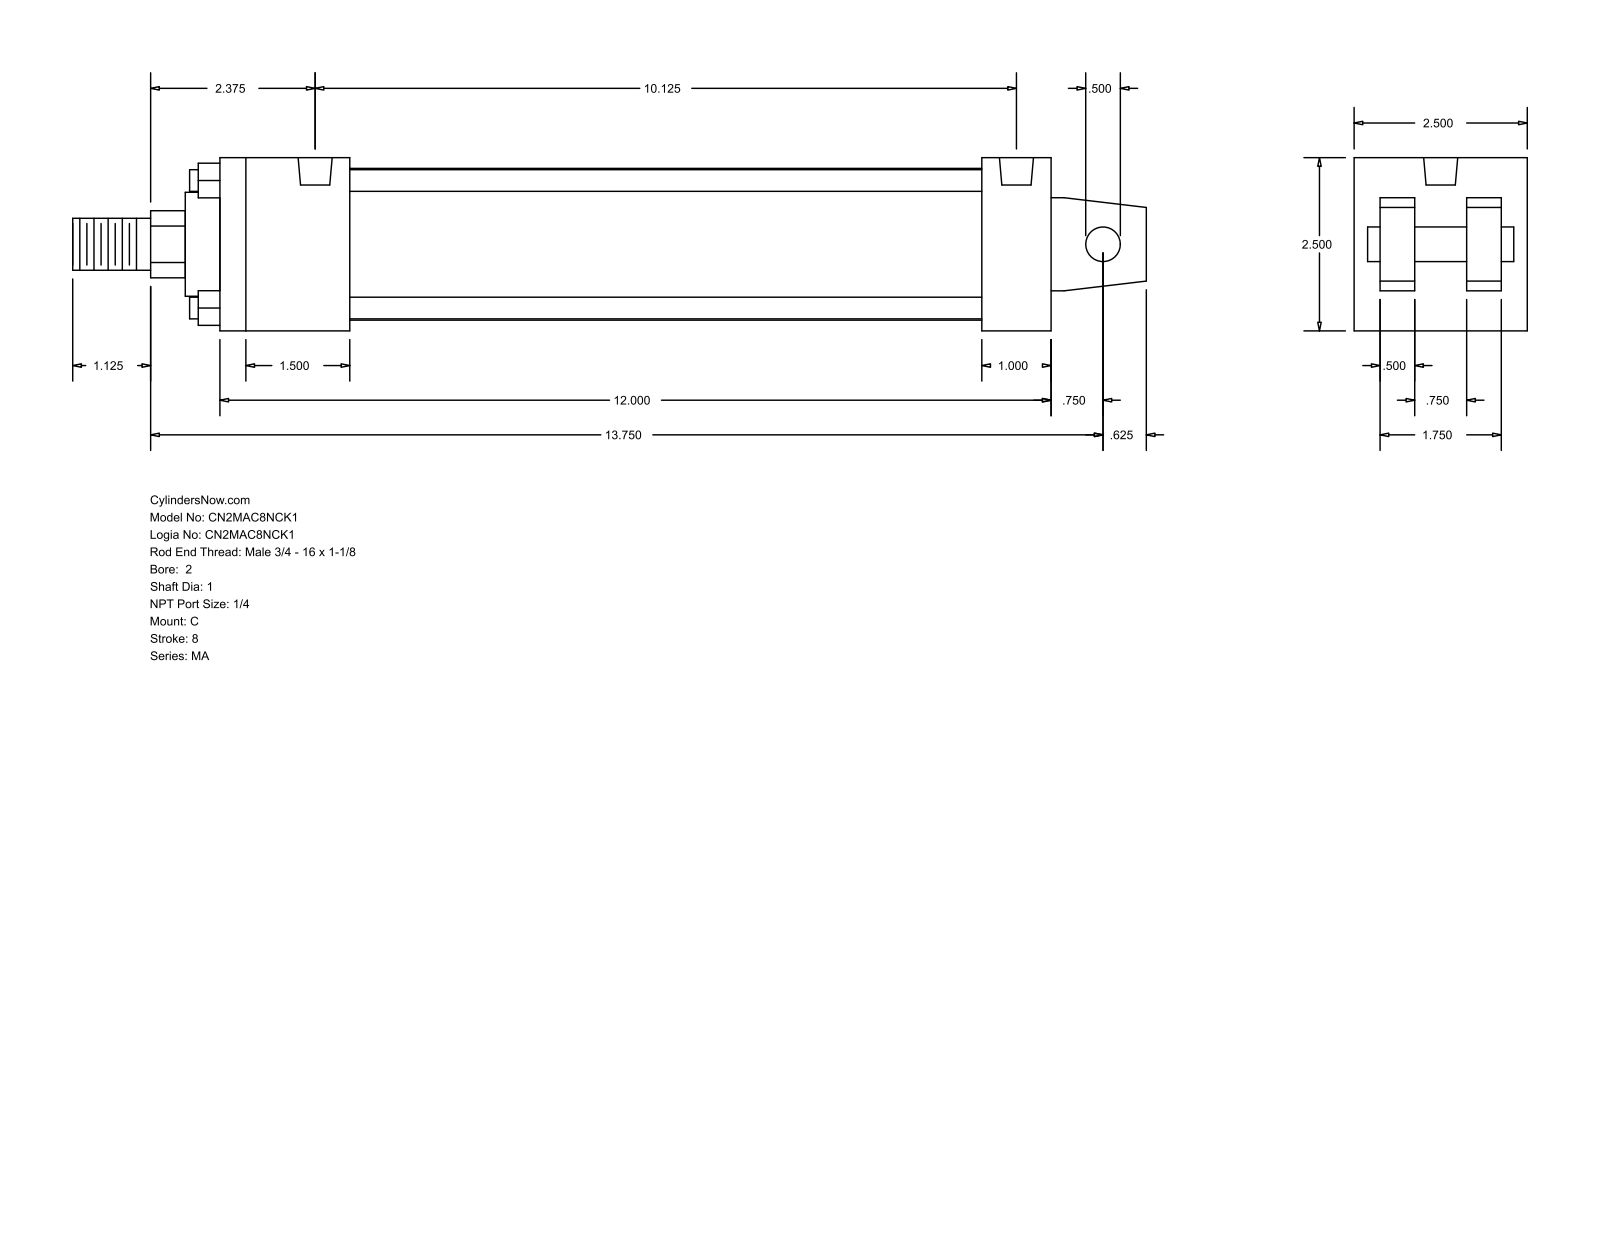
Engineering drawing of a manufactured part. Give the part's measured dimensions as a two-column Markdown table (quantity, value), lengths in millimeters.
| quantity | value |
| --- | --- |
| part name | MA_C__0200_1 |
| STEP written by | GSSL Pune (CONFIG_CONTROL_DESIGN) |
| units | millimeters |
| bodies | 0 solids, 103 faces (76 planar, 27 cylindrical, 0 other) |
| overall size | 393.7 × 63.5 × 63.5 |
| round holes (diameter × count) | 7.94 × 4, 12.49 × 2 |
| round bosses / shafts (diameter × count) | 7.94 × 4, 55.63 × 1, 38.1 × 1, 25.4 × 1, 19.05 × 1, 12.7 × 1 |
| partial cylindrical surfaces (radius × count) | 12.29 × 1 |
| main face-to-face distances | 63.5, 12.7, 304.8, 22.22, 41.28, 9.52, 53.98, 31.76, 47.63, 25.4 |
| hole center spacings | 257.17 |
